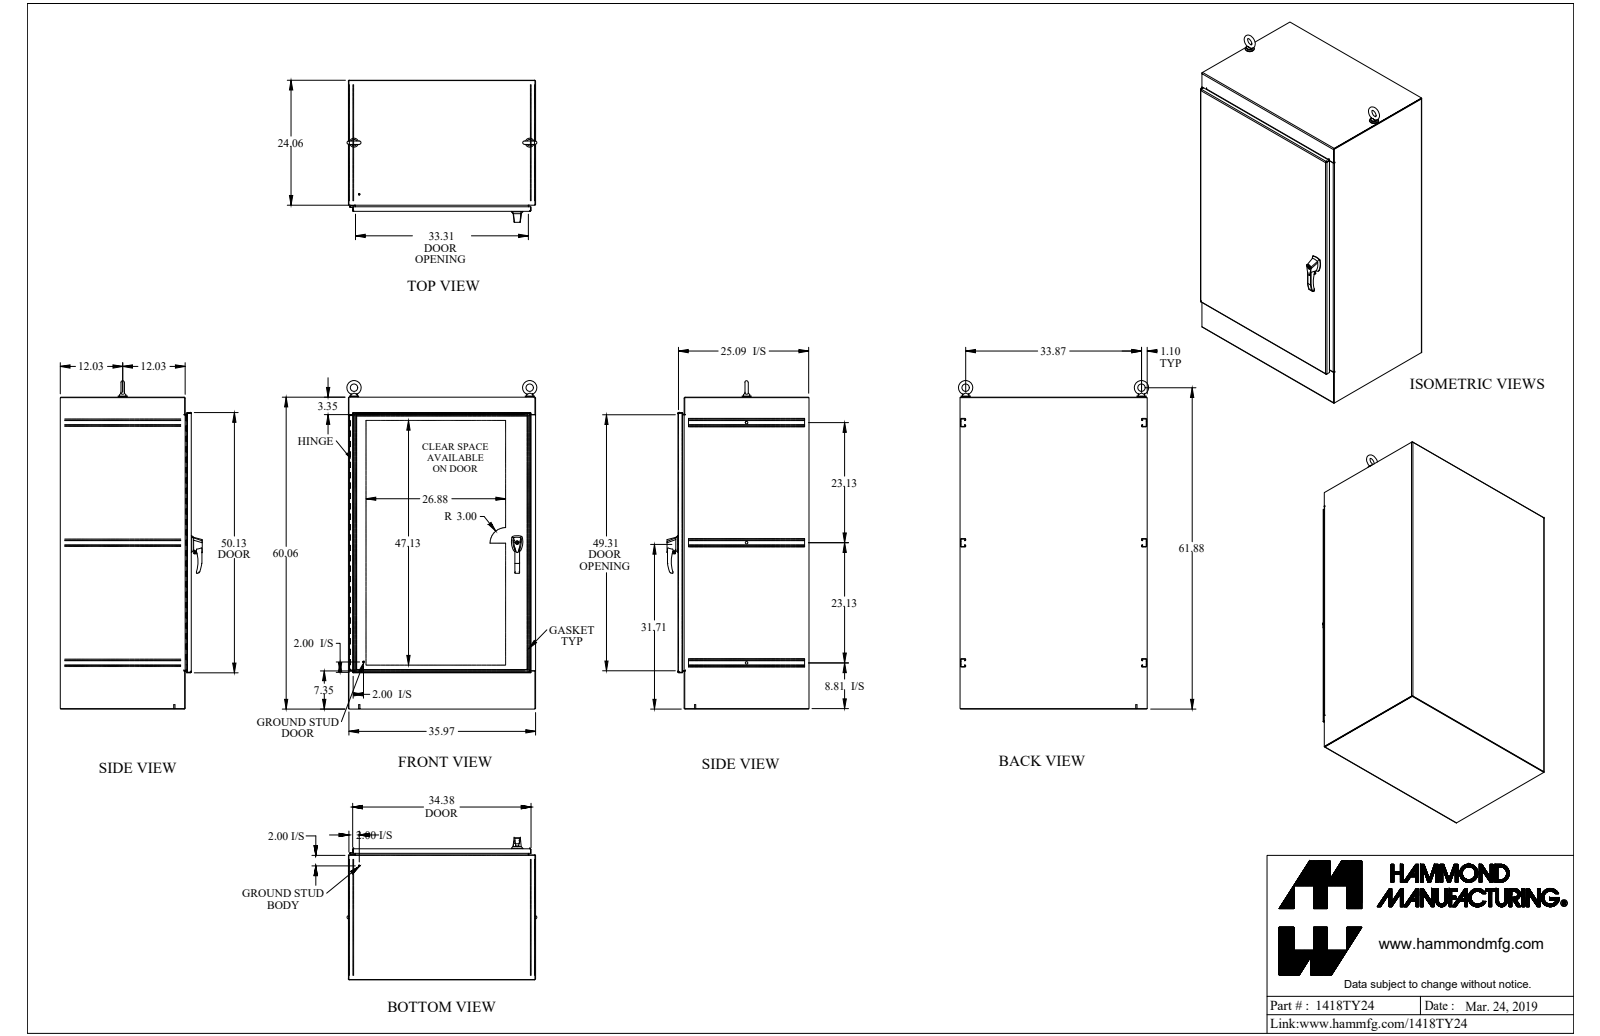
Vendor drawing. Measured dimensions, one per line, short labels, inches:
name: 1418TY24_Default
written by: SolidWorks 2019 (CONFIG_CONTROL_DESIGN)
unit: in
bodies: 52 solids, 2082 faces (914 planar, 1003 cylindrical, 165 other)
size: 63.713 × 37.118 × 27.363
volume: 1 011 in³; area: 21 255 in²
holes: 9× ⌀0.304, 4× ⌀0.75, 3× ⌀0.5, 2× ⌀0.25, 2× ⌀0.257, 2× ⌀0.28, 2× ⌀0.281, 2× ⌀0.313, 2× ⌀0.39, 2× ⌀0.413, 2× ⌀0.527, 2× ⌀0.625
bosses: 4× ⌀0.281, 2× ⌀1.75, 2× ⌀1.5, 2× ⌀1.25, 2× ⌀1, 2× ⌀0.75, 2× ⌀0.738, 2× ⌀0.63
rounds: 42× R0.043, 36× R0.138, 22× R0.125, 16× R0.018, 14× R0.048, 14× R0.143, 10× R0.06, 6× R0.015
face distances: 0.095, 35.965, 0.095, 25.057, 25.153, 59.965, 25.152, 25.248, 35.87, 36.06
hole spacings: 6, 12, 18, 24, 30, 33.87, 36, 0.03
